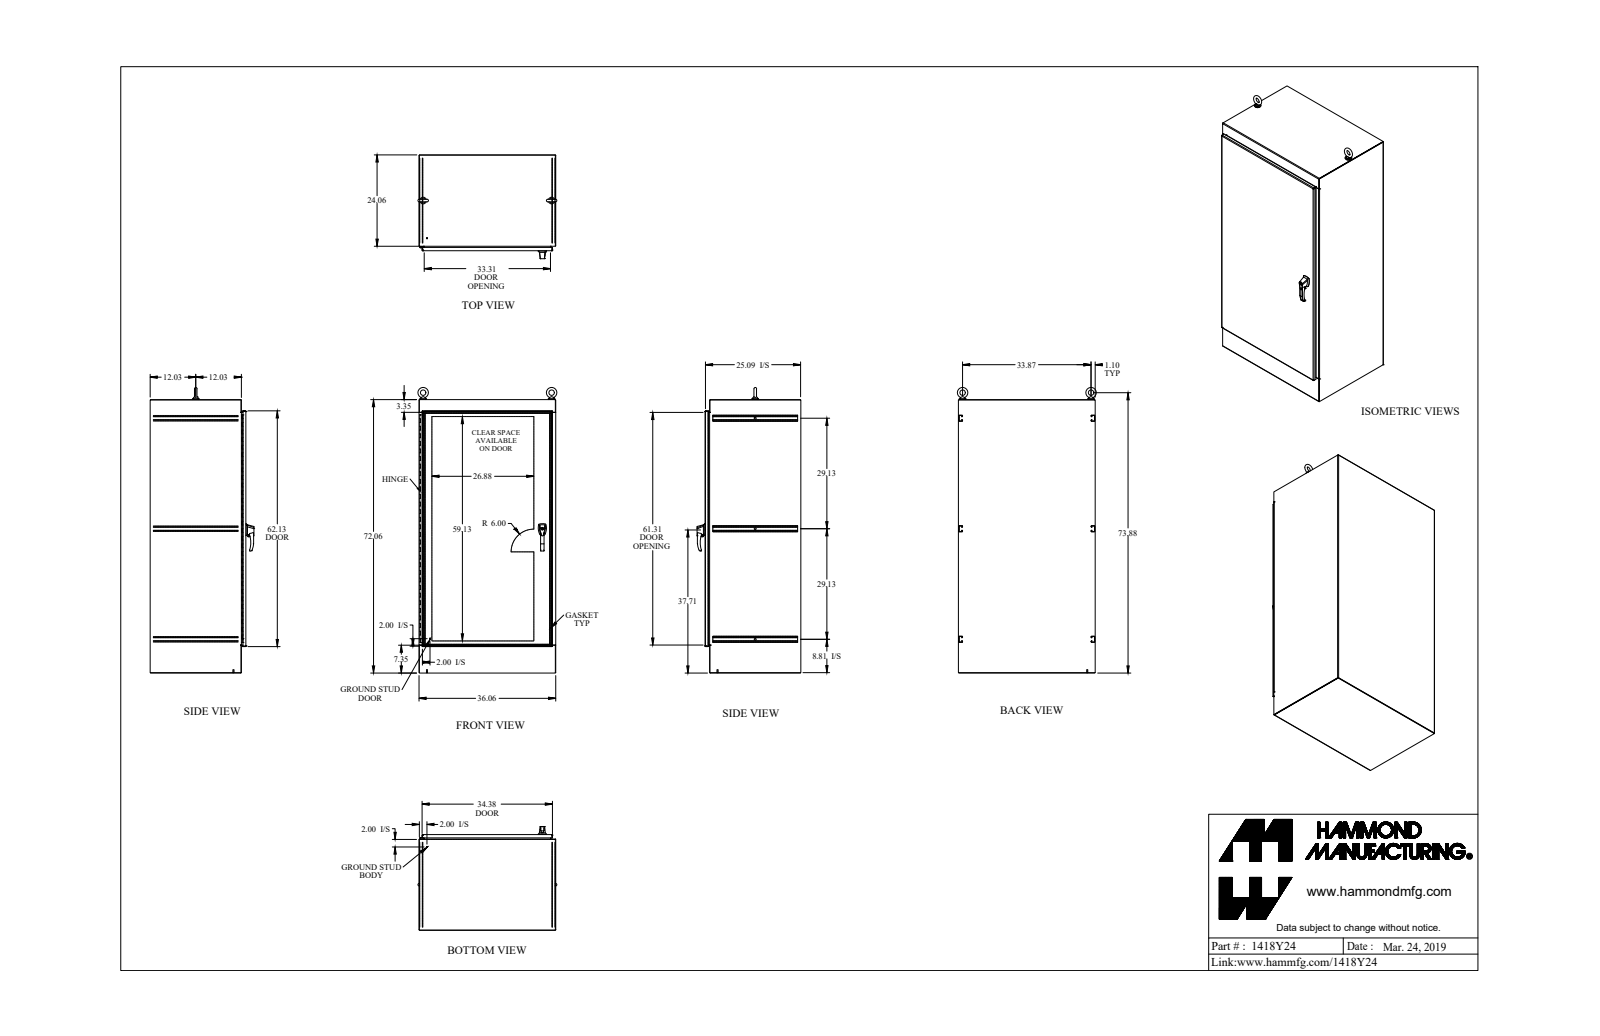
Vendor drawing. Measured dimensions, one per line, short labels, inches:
name: 1418Y24_Default
written by: SolidWorks 2019 (CONFIG_CONTROL_DESIGN)
unit: in
bodies: 52 solids, 1742 faces (781 planar, 796 cylindrical, 165 other)
size: 75.713 × 37.119 × 27.363
volume: 1 158 in³; area: 24 396 in²
holes: 10× ⌀0.304, 4× ⌀0.75, 3× ⌀0.5, 2× ⌀0.25, 2× ⌀0.257, 2× ⌀0.28, 2× ⌀0.281, 2× ⌀0.313, 2× ⌀0.39, 2× ⌀0.413, 2× ⌀0.527, 2× ⌀0.625
bosses: 4× ⌀0.281, 2× ⌀1.75, 2× ⌀1.5, 2× ⌀1.25, 2× ⌀1, 2× ⌀0.75, 2× ⌀0.738, 2× ⌀0.63
rounds: 42× R0.043, 36× R0.138, 22× R0.125, 16× R0.018, 14× R0.048, 14× R0.143, 10× R0.06, 7× R0.318
face distances: 0.095, 35.965, 0.095, 25.057, 25.153, 25.152, 25.248, 35.87, 71.965, 36.06
hole spacings: 6, 12, 18, 24, 30, 33.87, 36, 42
